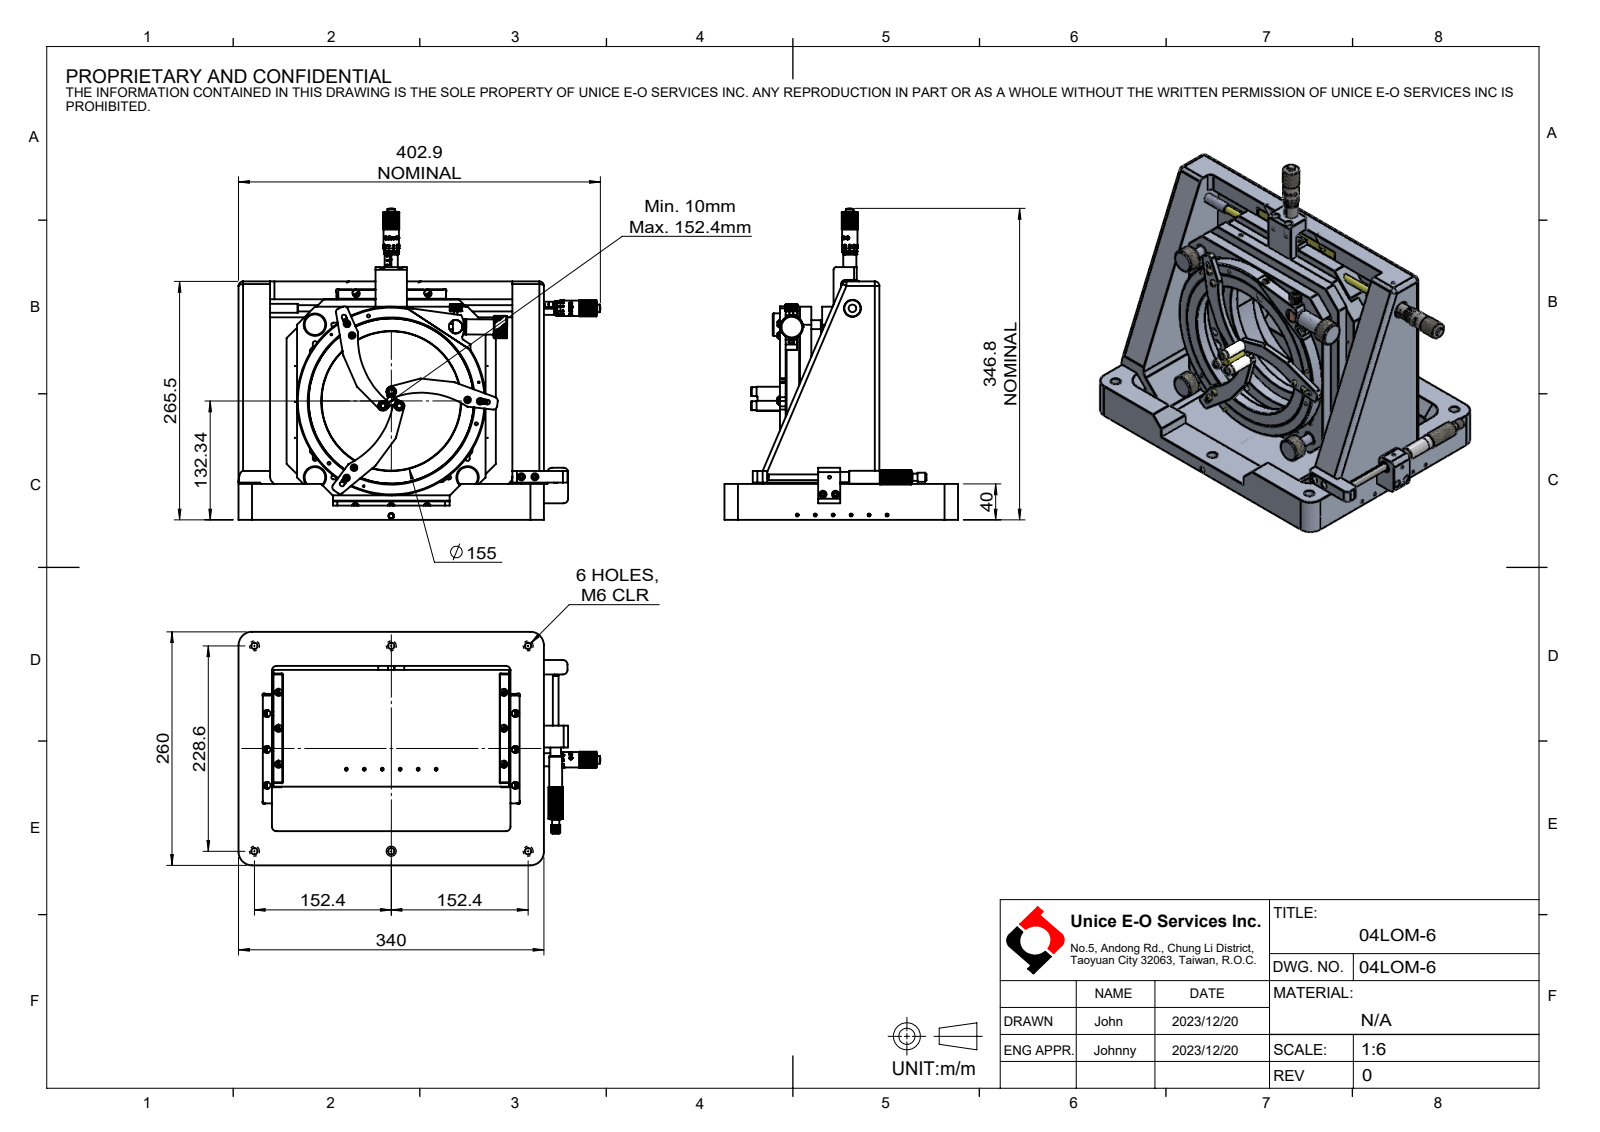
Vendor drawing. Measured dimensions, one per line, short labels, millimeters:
name: 04LOM-6
written by: SolidWorks 2022 (CONFIG_CONTROL_DESIGN)
unit: mm
bodies: 0 solids, 819 faces (345 planar, 359 cylindrical, 115 other)
size: 402.9 × 346.8 × 260
holes: 29× ⌀8, 21× ⌀3.3, 6× ⌀7.14, 6× ⌀11, 6× ⌀11.11, 4× ⌀15, 3× ⌀6.5, 2× ⌀4.2, 2× ⌀4.3, 2× ⌀178, 1× ⌀6, 1× ⌀7.2
bosses: 16× ⌀4, 11× ⌀6.5, 7× ⌀10, 6× ⌀7, 5× ⌀7.5, 4× ⌀25, 3× ⌀11, 3× ⌀2
rounds: 20× R5, 16× R0.1, 13× R2, 13× R4, 8× R2.25, 4× R1, 4× R2.5, 4× R3
face distances: 40, 51, 38, 13, 35, 0.5, 24.7, 12.7, 27, 305
hole spacings: 40, 20, 80, 98.49, 30, 60, 101.24, 139.28
